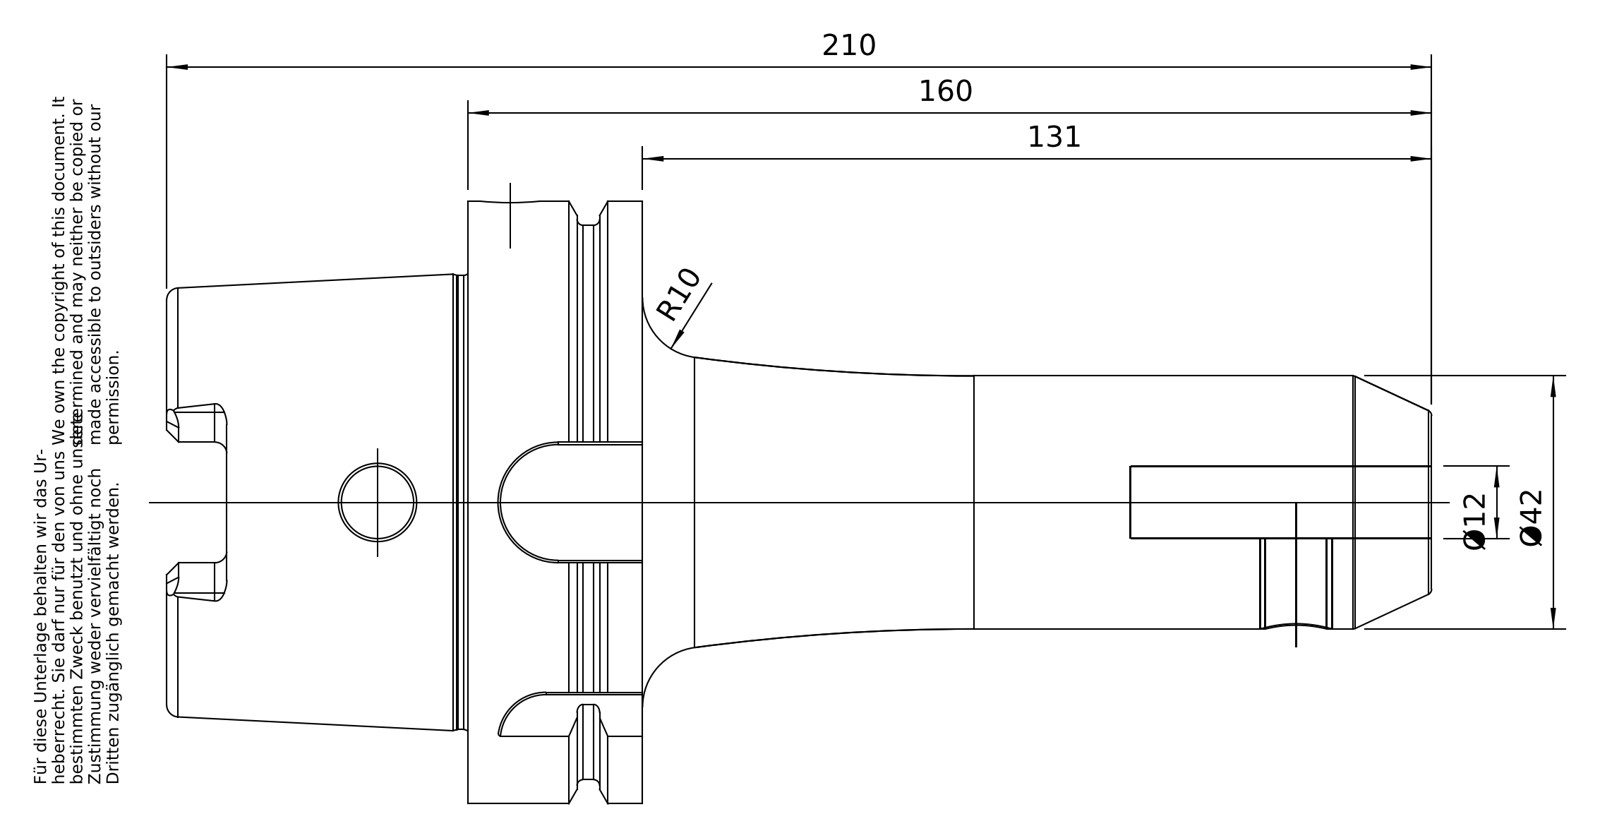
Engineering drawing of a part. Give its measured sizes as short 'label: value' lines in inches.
name: A100-002-12
written by: PRO/ENGINEER BY PARAMETRIC TECHNOLOGY CORPORATION, 2010430 (CONFIG_CONTROL_DESIGN)
unit: in
bodies: 1 solid, 182 faces (50 planar, 55 cylindrical, 77 other)
size: 8.268 × 3.937 × 3.937
volume: 26.72 in³; area: 107 in²
holes: 3× ⌀0.472, 1× ⌀0.394, 1× ⌀0.402, 1× ⌀0.886, 1× ⌀0.945, 1× ⌀0.957, 1× ⌀0.965, 1× ⌀2.087, 1× ⌀2.48
bosses: 1× ⌀3.937, 1× ⌀3.622, 1× ⌀2.967, 1× ⌀1.654
rounds: 6× R0.079, 4× R0.197, 1× R0.315, 1× R0.394, 1× R0.433
face distances: 1.142, 0.492, 0.65, 1.969, 2.461, 3.11, 6.299, 8.268, 5.807, 5.157
hole spacings: 5.138
